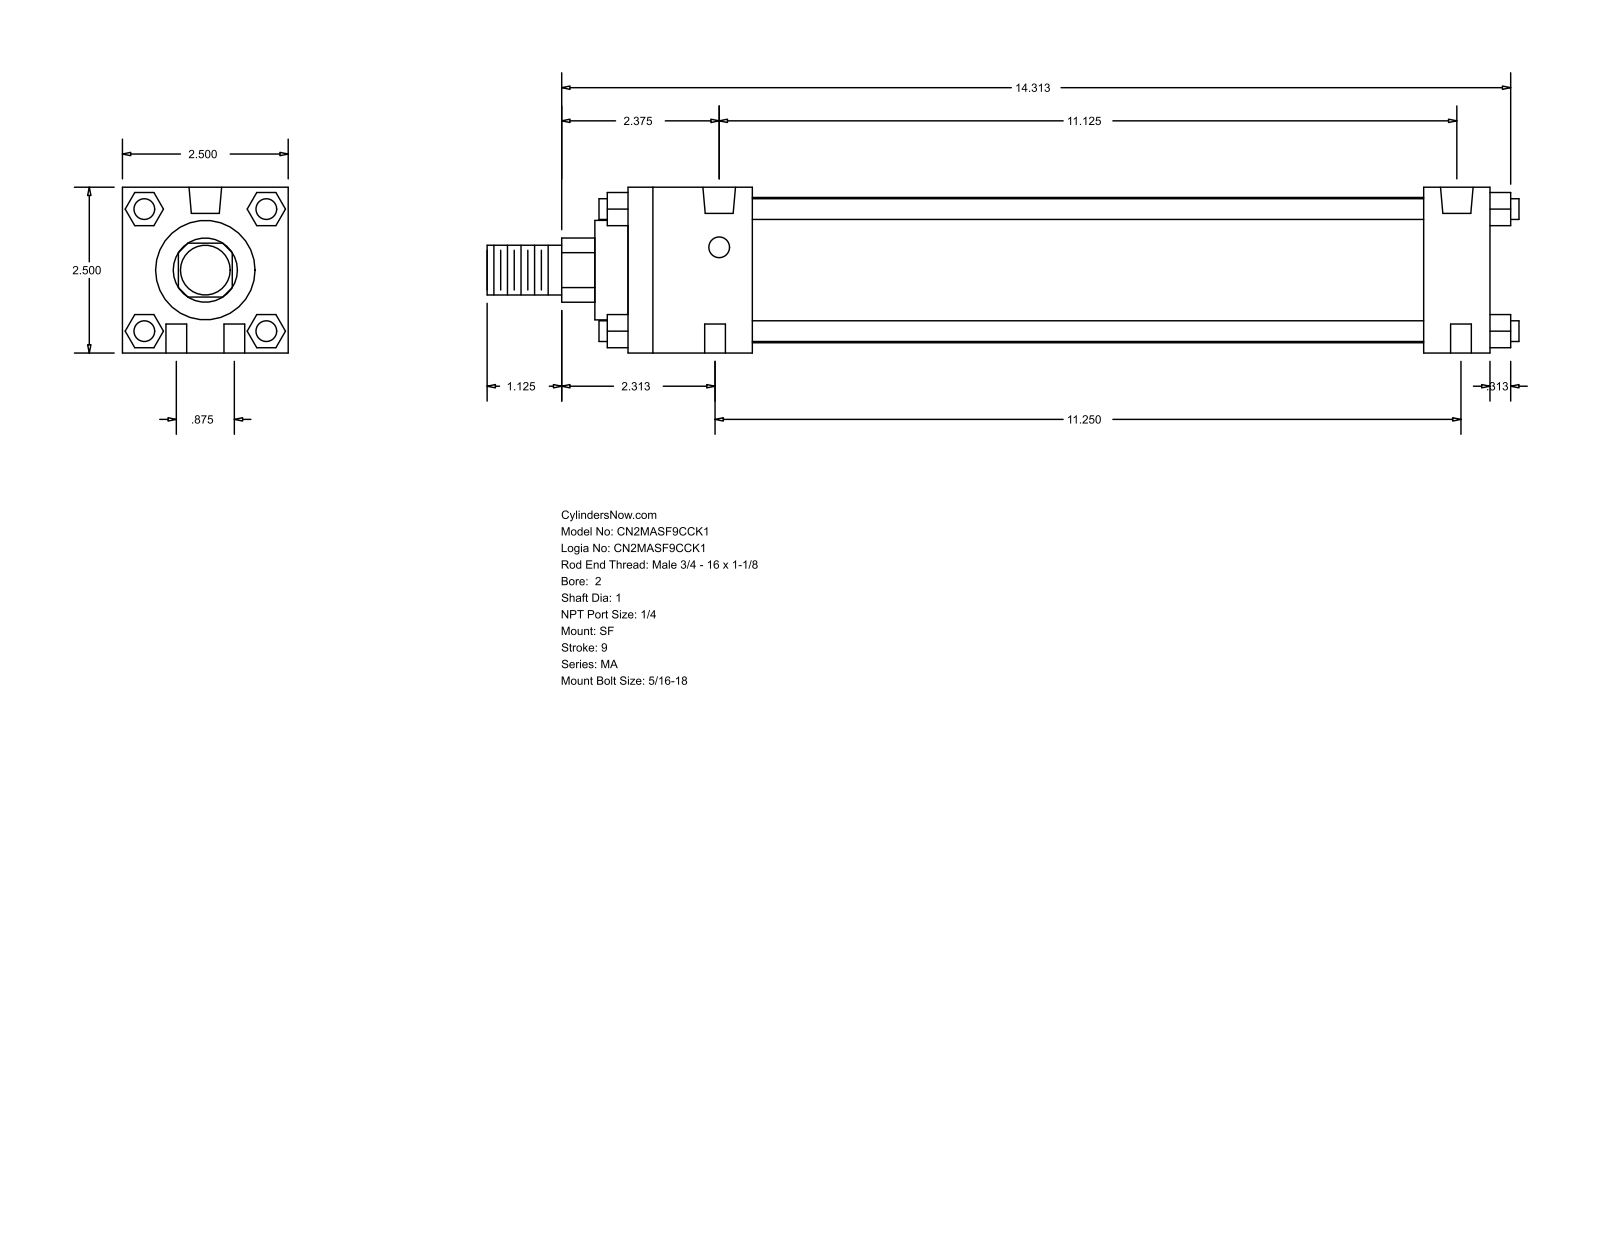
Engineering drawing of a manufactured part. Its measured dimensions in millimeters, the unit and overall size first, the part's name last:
Units: millimetres
Overall size (bounding box): 395.29 × 63.5 × 63.5
Round holes (diameter × count): ⌀7.94 ×6, ⌀12.49 ×2
Round bosses / shafts (diameter × count): ⌀7.94 ×4, ⌀55.63 ×1, ⌀38.1 ×1, ⌀25.4 ×1, ⌀19.05 ×1
Partial cylindrical surfaces — rounded edges, fillets, slot ends (radius × count): R12.29 ×1
Main face-to-face distances: 63.5, 330.2, 12.7, 25.4, 304.8, 47.63, 257.17, 282.57, 40.47, 23.37
Hole centre spacings: 11.22, 284.38, 22.22, 282.57, 285.75, 286.61
Bodies: 0 solids, 124 faces (94 planar, 30 cylindrical, 0 other)
Part name (STEP PRODUCT): MA_SF__0200_1
STEP written by: GSSL Pune (CONFIG_CONTROL_DESIGN)
